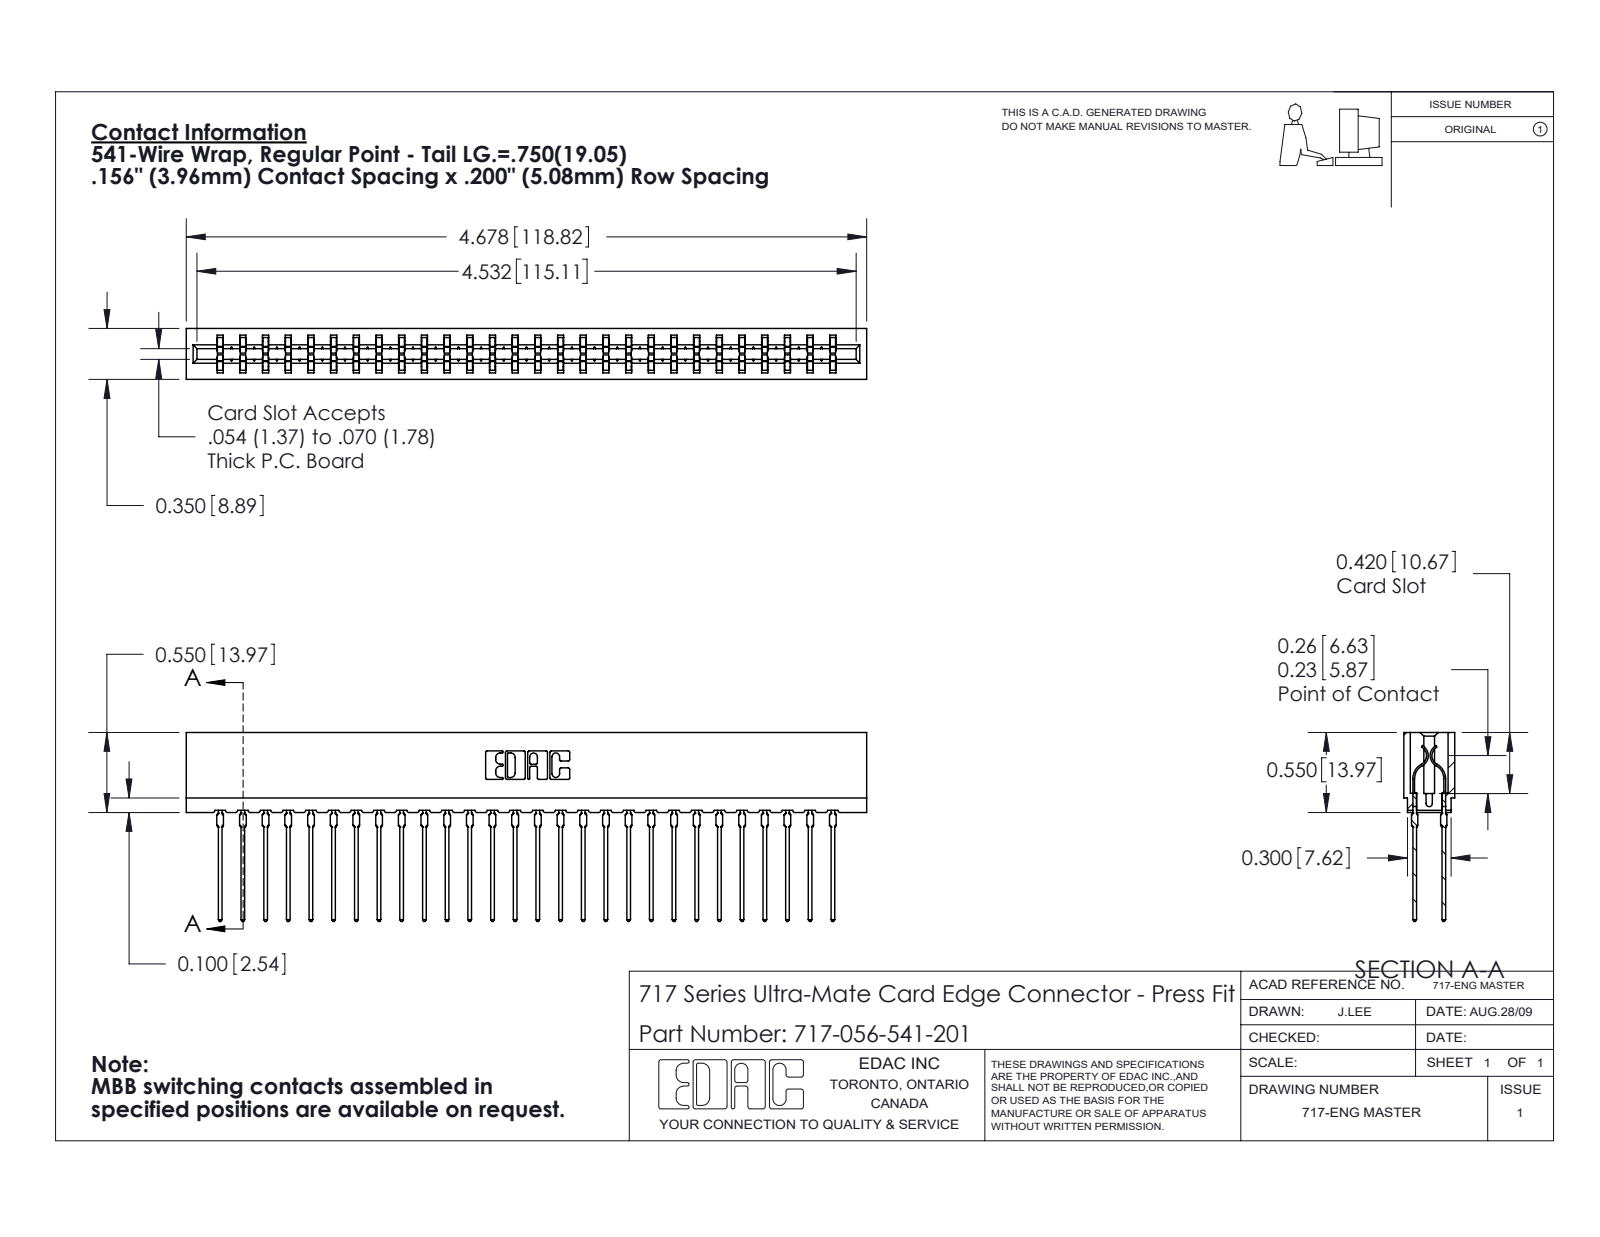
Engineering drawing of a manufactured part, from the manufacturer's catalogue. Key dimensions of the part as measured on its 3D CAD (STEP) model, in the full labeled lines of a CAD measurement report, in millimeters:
Part name (STEP PRODUCT): 717-056-541-201; 717 Part_Insulator Option - 06; 745-292-001_541
STEP written by: SolidWorks 2020 (CONFIG_CONTROL_DESIGN)
Units: millimetres
Bodies: 57 solids, 5134 faces (2658 planar, 1020 cylindrical, 1456 other)
Overall size (bounding box): 118.8 × 33 × 8.9
Volume: 10 600 mm³ · Surface area: 17 320 mm²
Partial cylindrical surfaces — rounded edges, fillets, slot ends (radius × count): R0.5 ×112, R0.4 ×56, R0.3 ×22, R0.1 ×8, R0.3 ×8, R0.2 ×6, R0.8 ×6, R0.7 ×3
Main face-to-face distances: 5.4, 3.5, 8.9, 1.6, 7.3, 1.9, 3.8, 2.2, 6.7, 0.6
